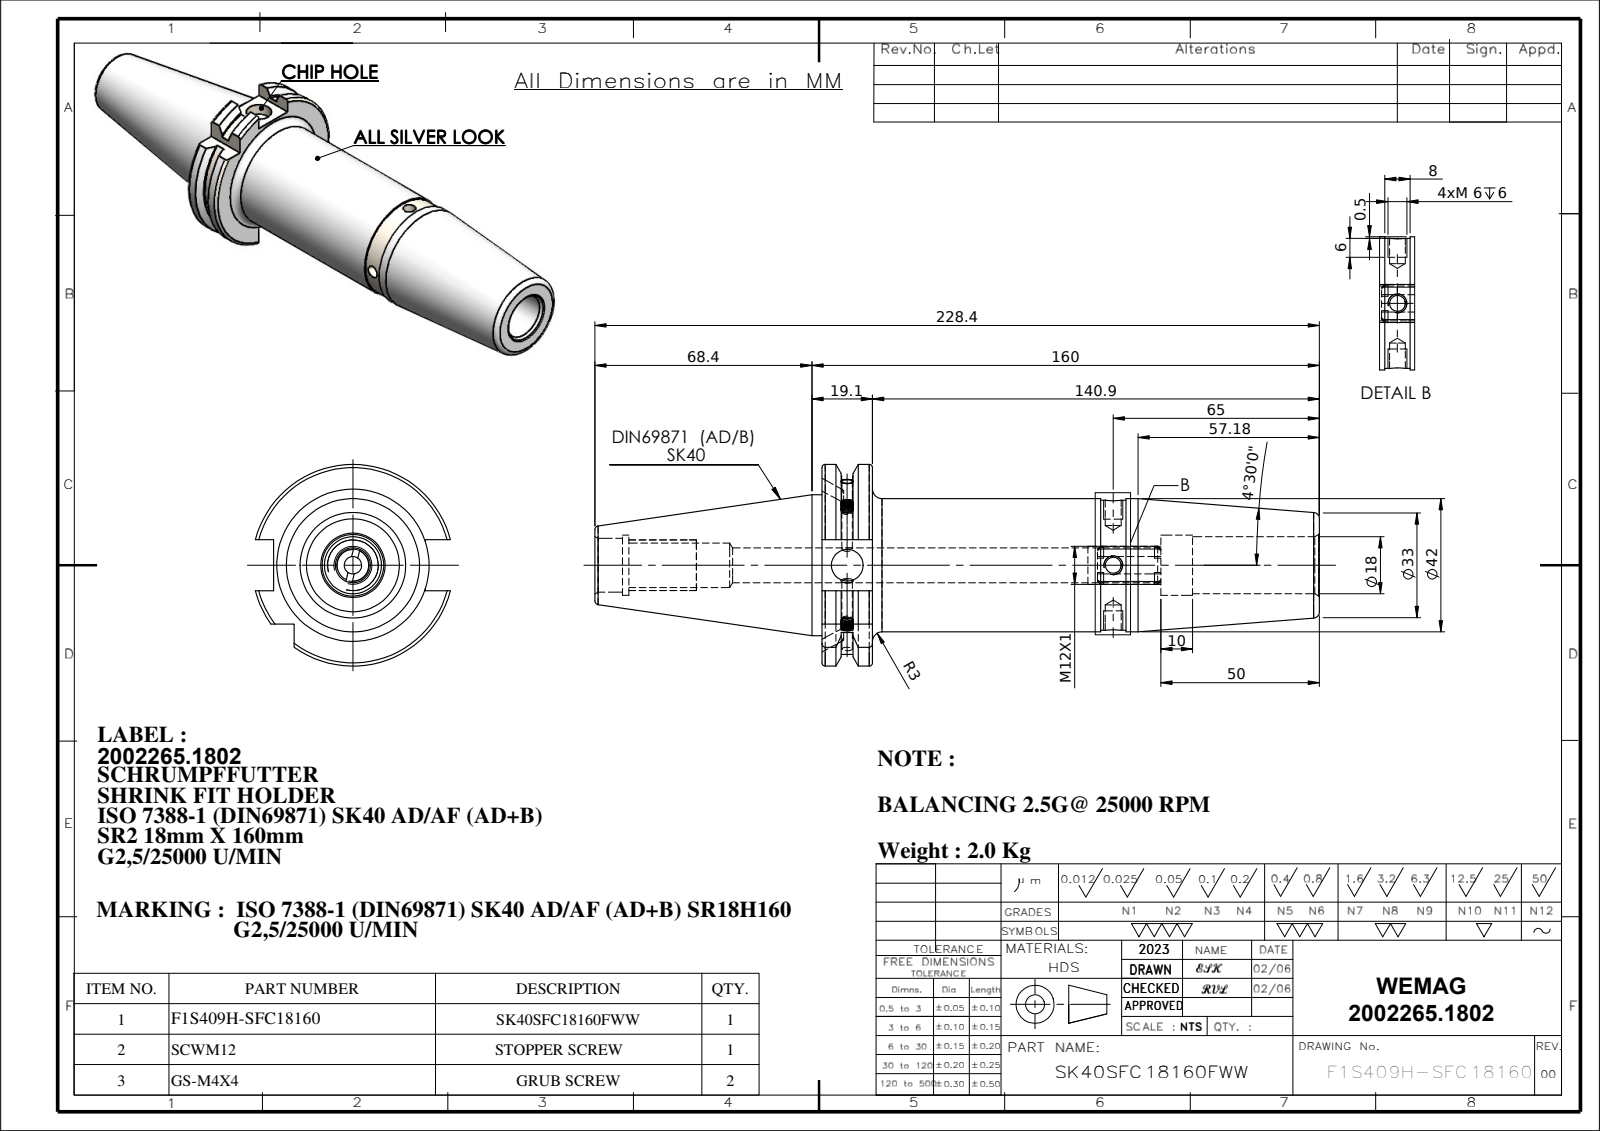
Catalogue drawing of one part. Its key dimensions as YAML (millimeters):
part_name: "SCWM12; SK40SFC18160FWW; GS-M4X4_DIN 913 - M4 x 4-N; 91406-SR218160"
step_written_by: "SolidWorks 2018 (CONFIG_CONTROL_DESIGN)"
units: millimeters
bodies: {solids: 4, faces: 243, planar: 67, cylindrical: 70, other: 106}
overall_size: [228.4, 63.55, 61.48]
volume: 259447
surface_area: 46106
round_holes:
  - {diameter: 5, count: 2}
  - {diameter: 3.3, count: 1}
  - {diameter: 5.5, count: 1}
  - {diameter: 10, count: 1}
  - {diameter: 11, count: 1}
  - {diameter: 14, count: 1}
  - {diameter: 17, count: 1}
  - {diameter: 17.99, count: 1}
  - {diameter: 18.99, count: 1}
  - {diameter: 19, count: 1}
round_bosses_or_shafts:
  - {diameter: 4, count: 2}
  - {diameter: 44.45, count: 1}
  - {diameter: 42, count: 1}
  - {diameter: 41, count: 1}
  - {diameter: 12, count: 1}
partial_cylinders:
  - {radius: 28.12, count: 1}
  - {radius: 31.77, count: 1}
face_to_face_distances: [15.9, 156.8, 140.9, 106.8, 90.9, 50, 16.1, 47.8, 167.7, 71.6]
hole_center_spacings: [83.85]
